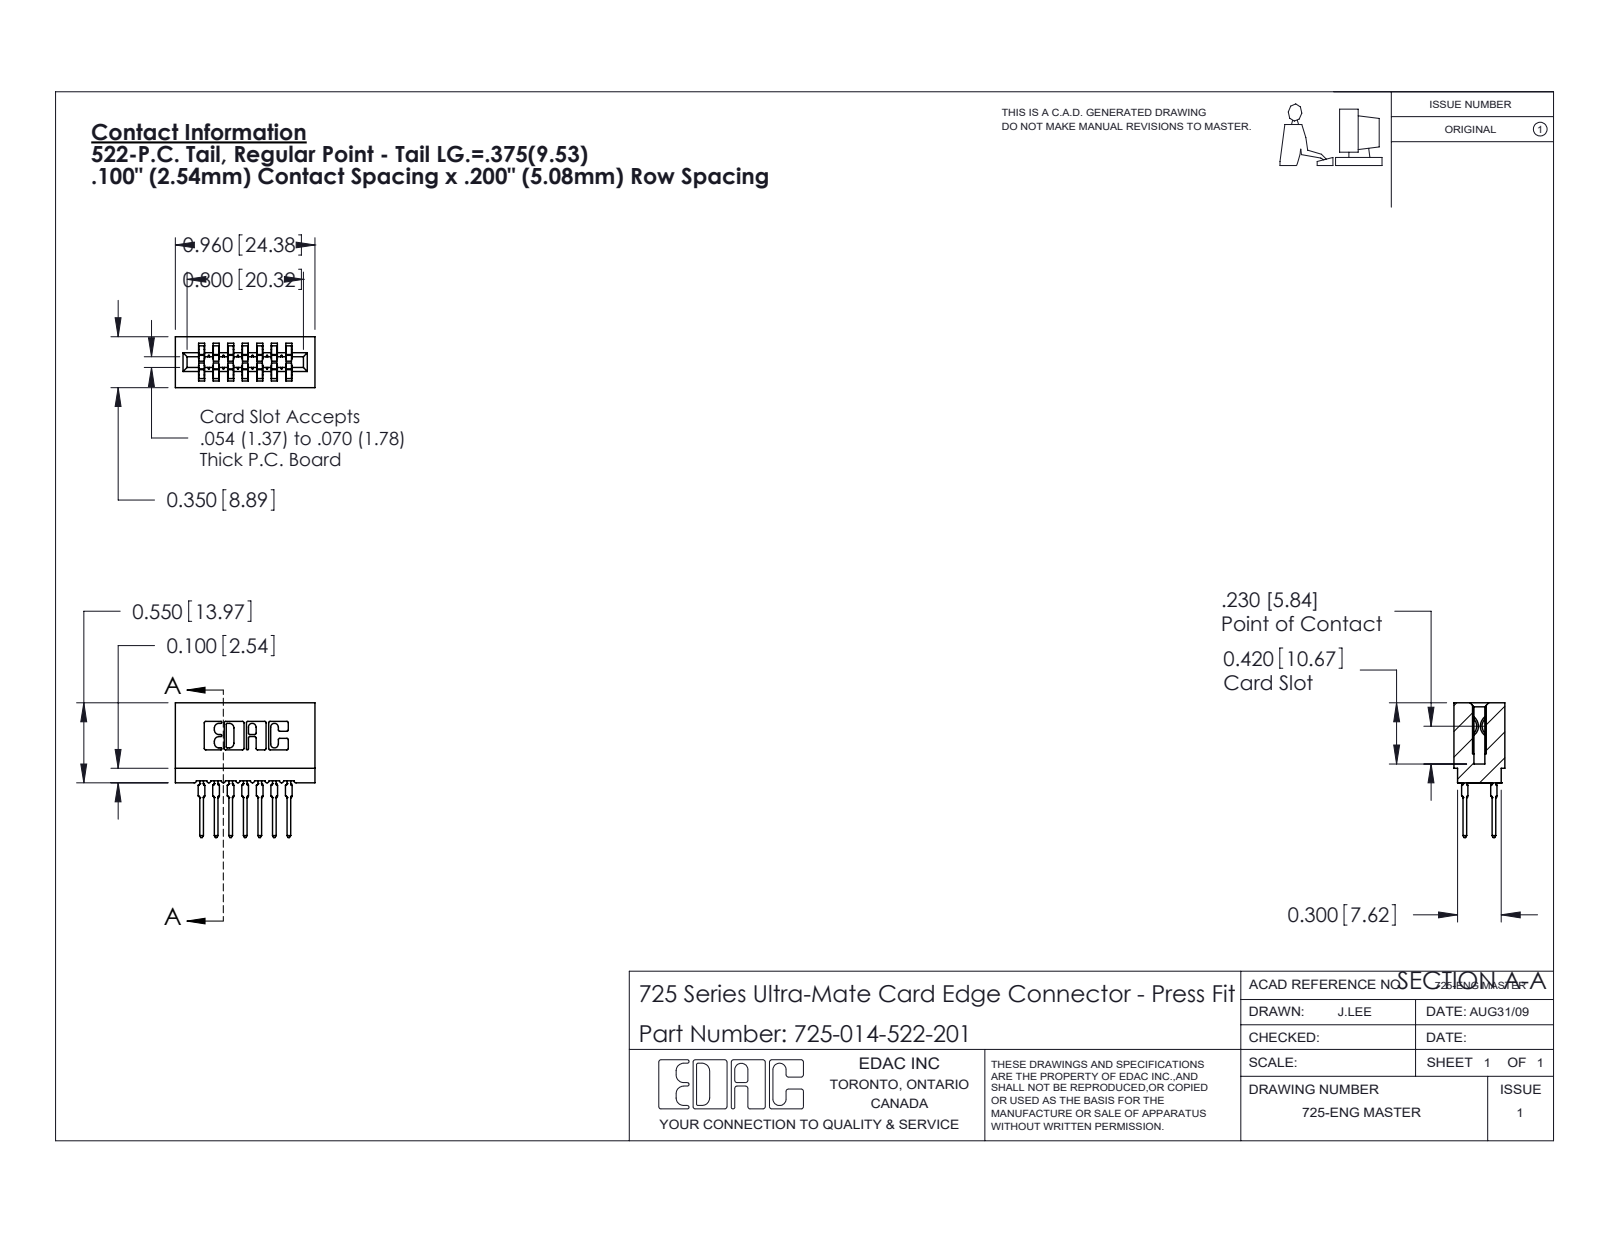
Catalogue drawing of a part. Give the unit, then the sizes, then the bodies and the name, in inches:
Units: inches
Overall size (bounding box): 0.96 × 0.926 × 0.35
Partial cylindrical surfaces — rounded edges, fillets, slot ends (radius × count): R0.021 ×28, R0.01 ×22, R0.015 ×14, R0.005 ×8, R0.011 ×8, R0.007 ×6, R0.031 ×6, R0.026 ×3
Main face-to-face distances: 0.1, 0.2, 0.3, 0.042, 0.4, 0.142, 0.058, 0.242, 0.158, 0.5
Volume: 0.13 in³ · Surface area: 5.876 in²
Bodies: 15 solids, 1348 faces (699 planar, 285 cylindrical, 364 other)
Part name (STEP PRODUCT): 725 Part_Insulator Option - 01; 745-292-001_522; 725-014-522-201
STEP written by: SolidWorks 2020 (CONFIG_CONTROL_DESIGN)
